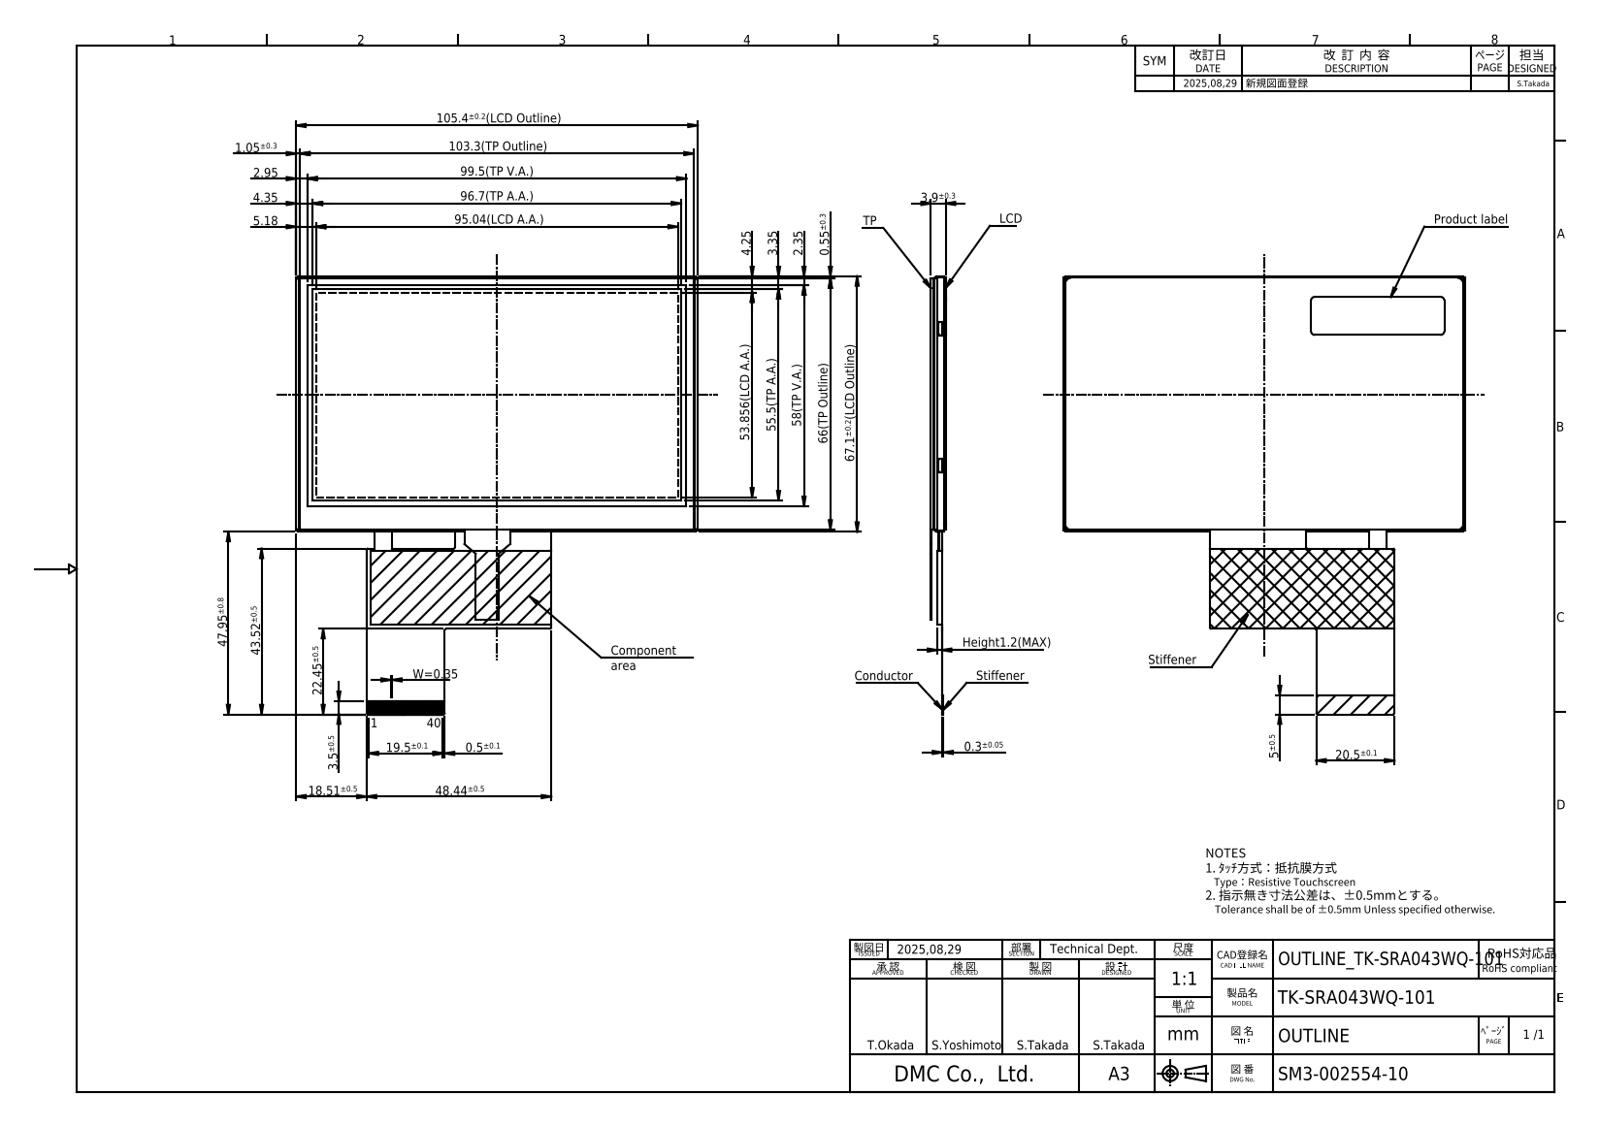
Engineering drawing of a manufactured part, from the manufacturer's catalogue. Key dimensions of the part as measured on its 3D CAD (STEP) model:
Part name (STEP PRODUCT): HP_TK-SRA043WQ-101
STEP written by: Autodesk Inventor 2024 (AUTOMOTIVE_DESIGN)
Units: millimetres
Bodies: 1 solid, 349 faces (308 planar, 33 cylindrical, 8 other)
Overall size (bounding box): 115.05 × 105.4 × 4
Volume: 26 305 mm³ · Surface area: 31 234 mm²
Partial cylindrical surfaces — rounded edges, fillets, slot ends (radius × count): R0.4 ×10, R0.5 ×4, R0.8 ×4, R1 ×4, R1.6 ×4, R0.4 ×1
Main face-to-face distances: 3.9, 3, 0.9, 0.4, 1.3, 2.6, 0.8, 2.2, 1.7, 1.6
